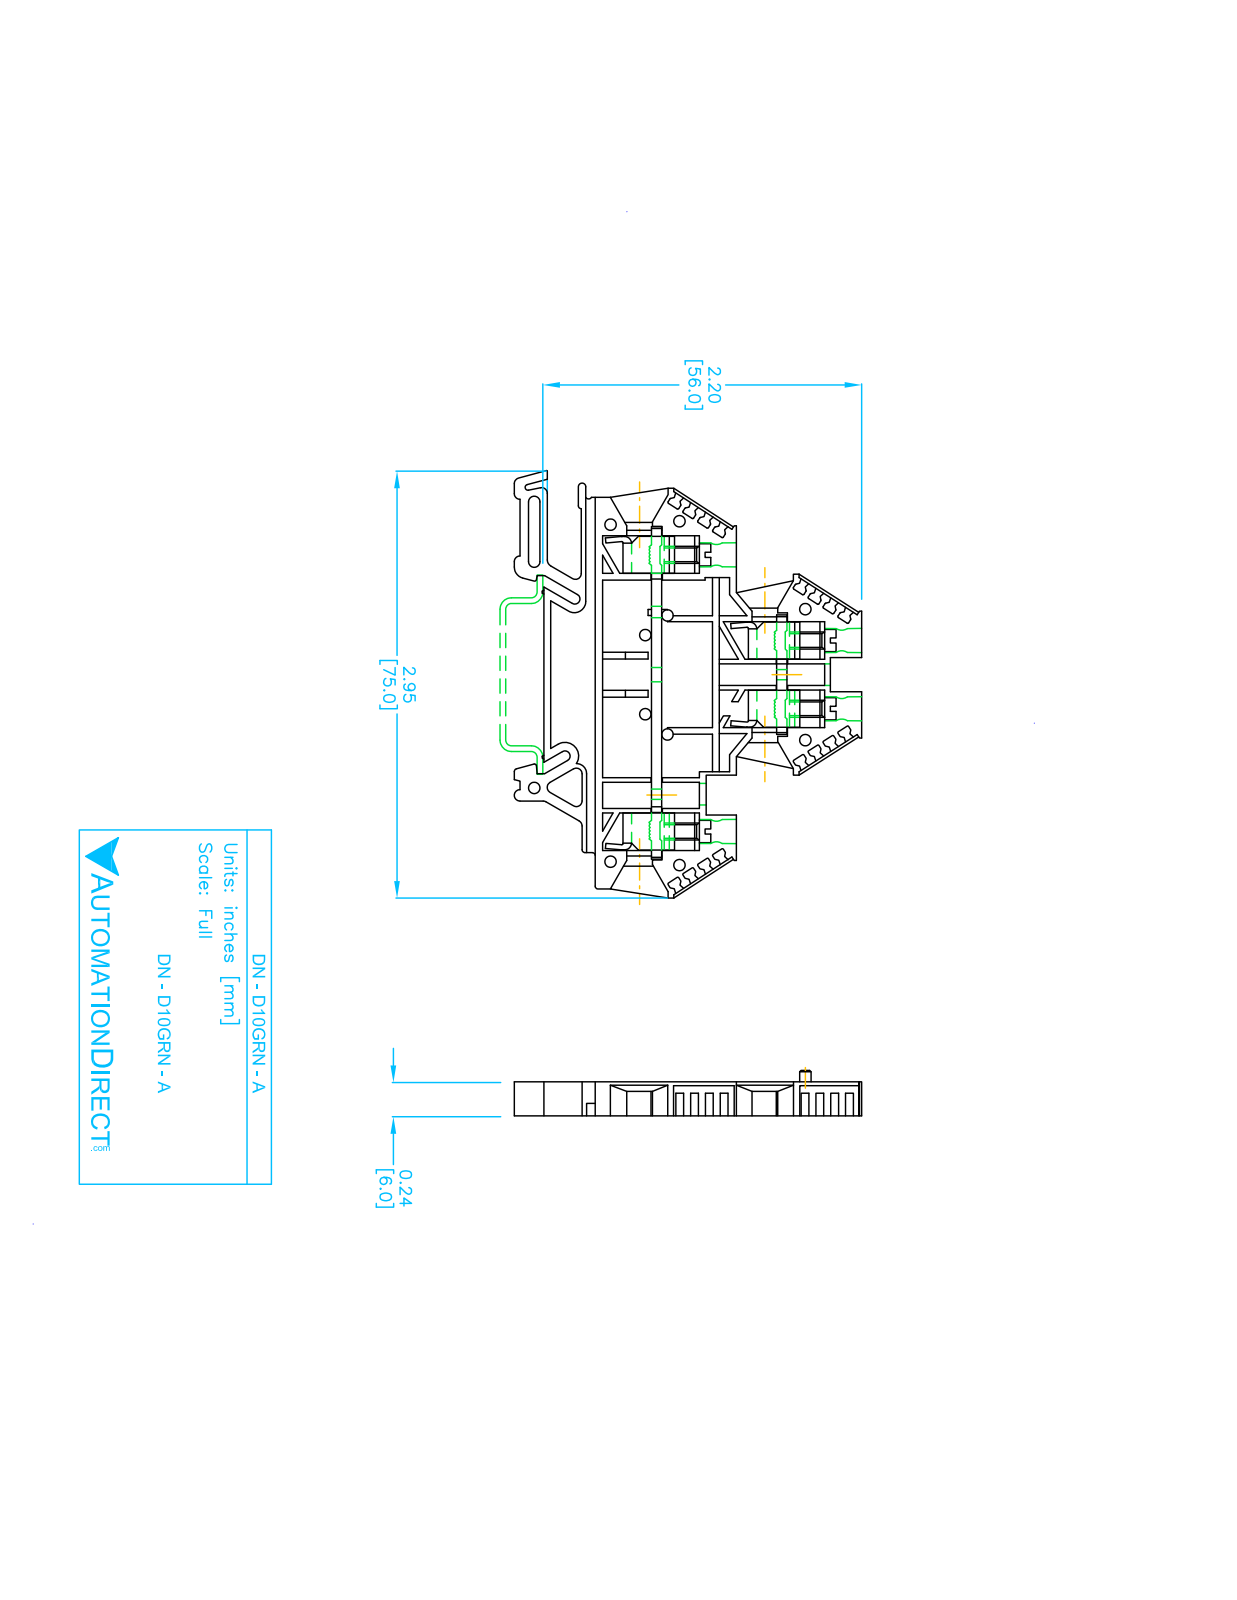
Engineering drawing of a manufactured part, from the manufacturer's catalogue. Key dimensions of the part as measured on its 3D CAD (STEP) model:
Part name (STEP PRODUCT): DN-D10GRN-A
STEP written by: SolidWorks 2017 (AUTOMOTIVE_DESIGN)
Units: inches
Bodies: 1 solid, 402 faces (261 planar, 141 cylindrical, 0 other)
Overall size (bounding box): 2.957 × 2.402 × 0.236
Volume: 0.9 in³ · Surface area: 14.85 in²
Round holes (diameter × count): ⌀0.165 ×4, ⌀0.079 ×1
Round bosses / shafts (diameter × count): ⌀0.146 ×4
Partial cylindrical surfaces — rounded edges, fillets, slot ends (radius × count): R0.008 ×64, R0.039 ×13, R0.02 ×6, R0.012 ×2, R0.035 ×2, R0.075 ×2, R0.079 ×2, R0.004 ×1
Main face-to-face distances: 0.236, 0.079, 0.157, 0.354, 0.059, 0.024, 0.031, 0.047, 0.976, 0.071
Hole centre spacings: 0.472, 0.593, 0.848, 1.065, 1.321, 1.913
